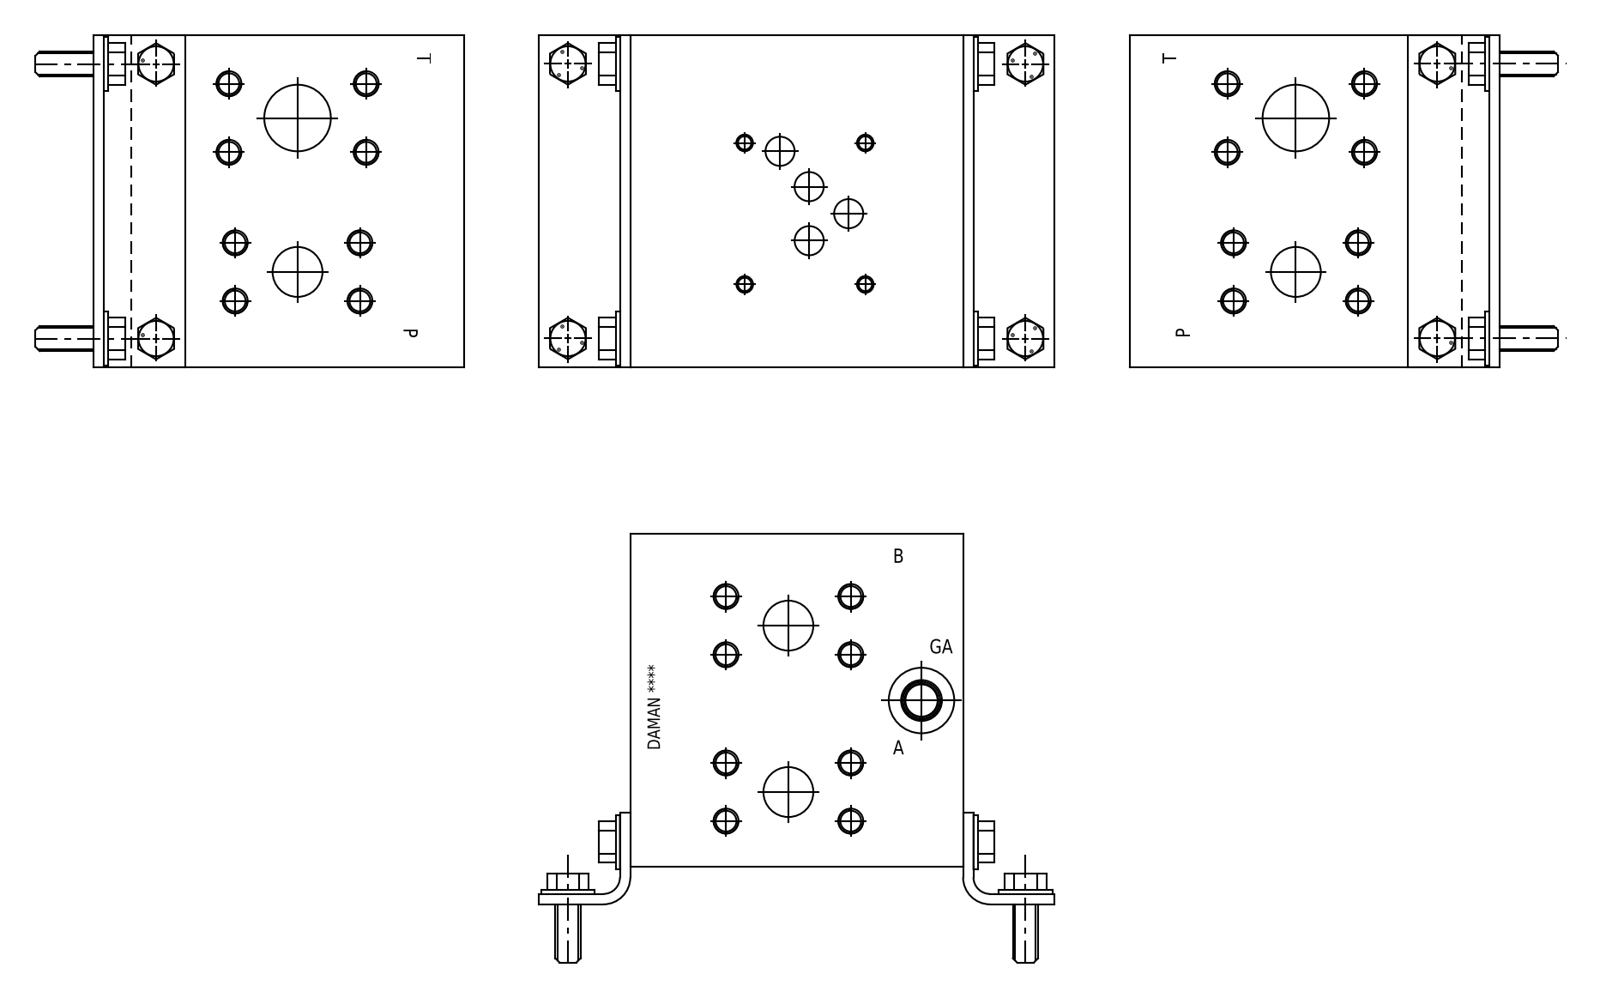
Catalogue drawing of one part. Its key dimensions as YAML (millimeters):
part_name: "Part_AD05HP015F_3D"
step_written_by: "Autodesk Inventor 2021 (AUTOMOTIVE_DESIGN)"
units: millimeters
bodies: {solids: 1, faces: 596, planar: 352, cylindrical: 79, other: 165}
overall_size: [146.05, 127, 127]
volume: 2280000
surface_area: 133275
round_holes:
  - {diameter: 7.92, count: 20}
  - {diameter: 9.53, count: 20}
  - {diameter: 5.11, count: 4}
  - {diameter: 6.35, count: 4}
  - {diameter: 11.13, count: 4}
  - {diameter: 19.05, count: 3}
  - {diameter: 12.29, count: 1}
  - {diameter: 12.9, count: 1}
  - {diameter: 14.27, count: 1}
  - {diameter: 14.53, count: 1}
  - {diameter: 25.02, count: 1}
  - {diameter: 25.4, count: 1}
face_to_face_distances: [127, 146.05, 22.1, 123.95, 0.79, 126.21, 104.9, 22.06, 126.96, 101.85]
hole_center_spacings: [26.26, 47.6, 78.3, 22.19, 26.25, 29.27, 47.59, 52.51]
